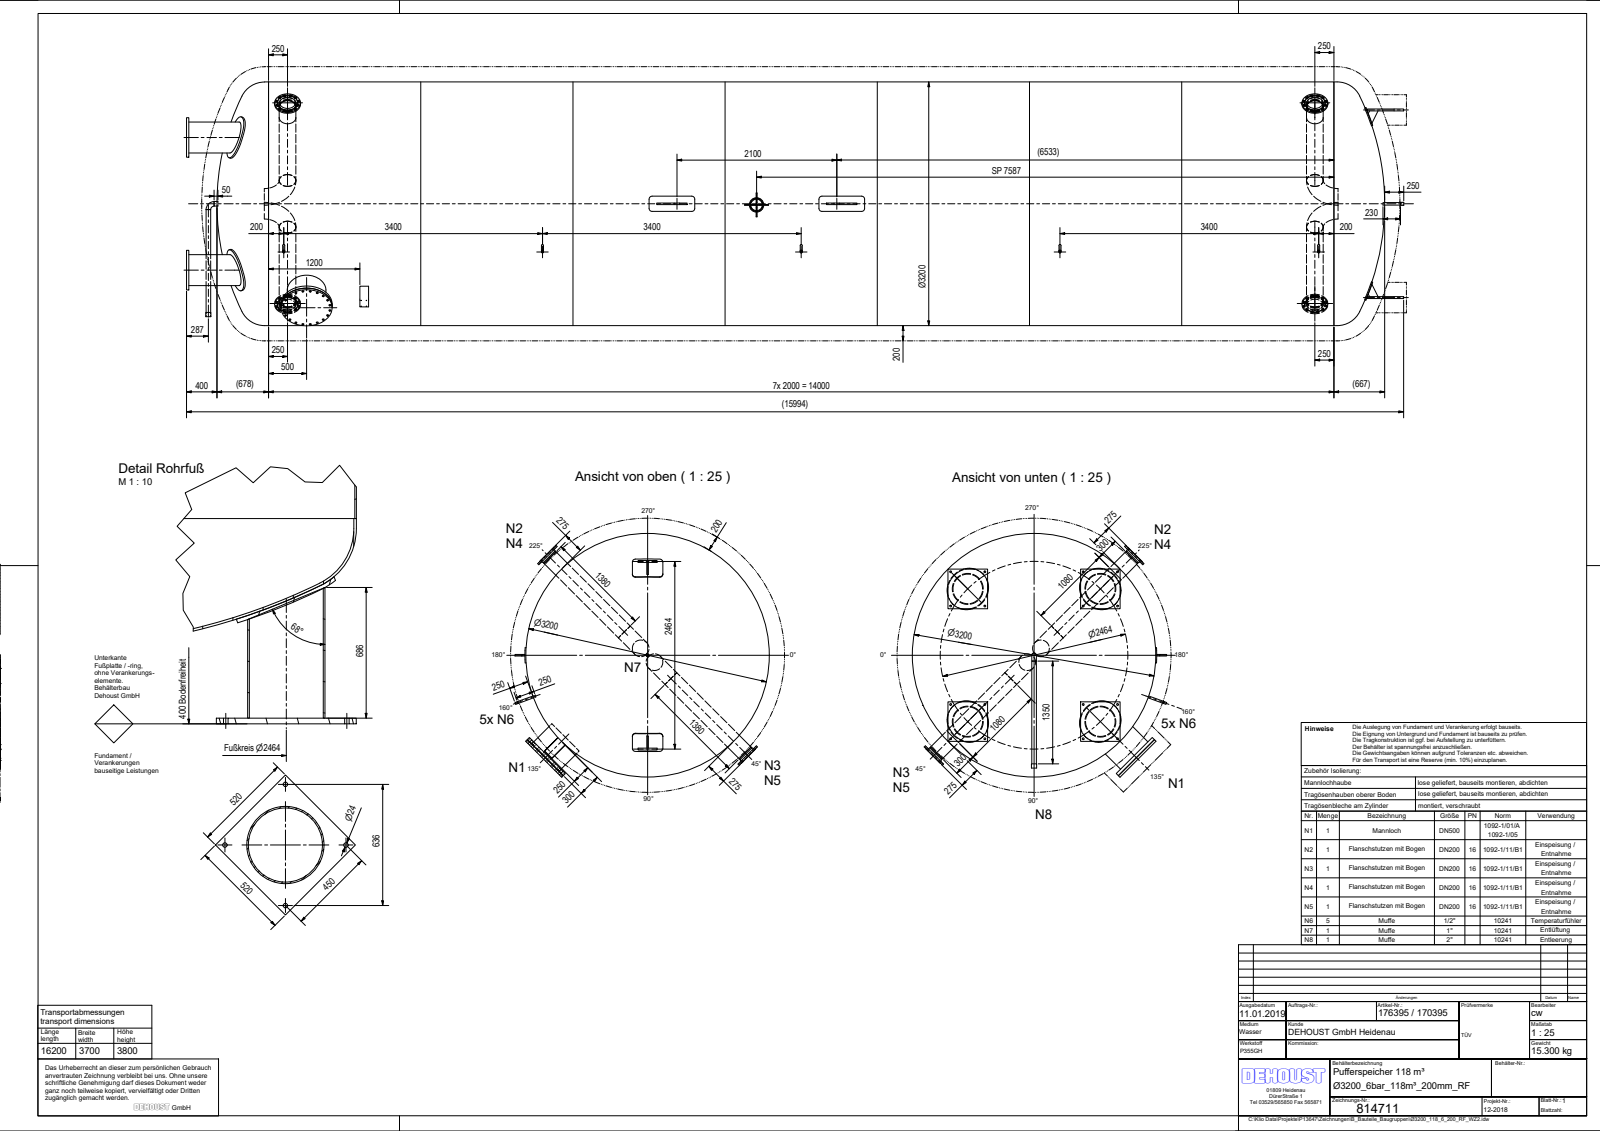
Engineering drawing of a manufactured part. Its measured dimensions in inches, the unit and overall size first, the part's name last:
Units: inches
Overall size (bounding box): 629.745 × 141.455 × 126.075
Round holes (diameter × count): ⌀0.866 ×48, ⌀1.024 ×40, ⌀0.945 ×16, ⌀0.733 ×5, ⌀0.854 ×5, ⌀1.059 ×5, ⌀0.228 ×4, ⌀8.13 ×4, ⌀8.161 ×4, ⌀8.626 ×4, ⌀15.307 ×4, ⌀2.059 ×2
Round bosses / shafts (diameter × count): ⌀8.626 ×8, ⌀1.059 ×5, ⌀1.039 ×5, ⌀22.047 ×4, ⌀16 ×4, ⌀13.386 ×4, ⌀10.551 ×4, ⌀26.378 ×2
Partial cylindrical surfaces — rounded edges, fillets, slot ends (radius × count): R1.575 ×8, R1.654 ×8, R0.197 ×2, R0.394 ×2, R2.835 ×2, R4.921 ×1, R63.346 ×1, R63.465 ×1
Main face-to-face distances: 23.622, 1.181, 257.087, 294.094, 299.539, 336.546, 298.357, 335.365, 37.008, 1.102
Hole centre spacings: 5.807, 12.205, 7.543, 133.858, 19.748, 5.807, 267.717, 14.348
Volume: 113 700 in³ · Surface area: 547 500 in²
Bodies: 65 solids, 516 faces (225 planar, 241 cylindrical, 50 other)
Part name (STEP PRODUCT): Ø3200_118_6_200_RF_WZ2; Klöpper_Gew_Ø3200_10,6; Klöpper_Gew_Ø3200_13,0; Zyl_Ø3200_8x14000_2019 (+8 more)
STEP written by: Autodesk Inventor 2019 (AUTOMOTIVE_DESIGN)
